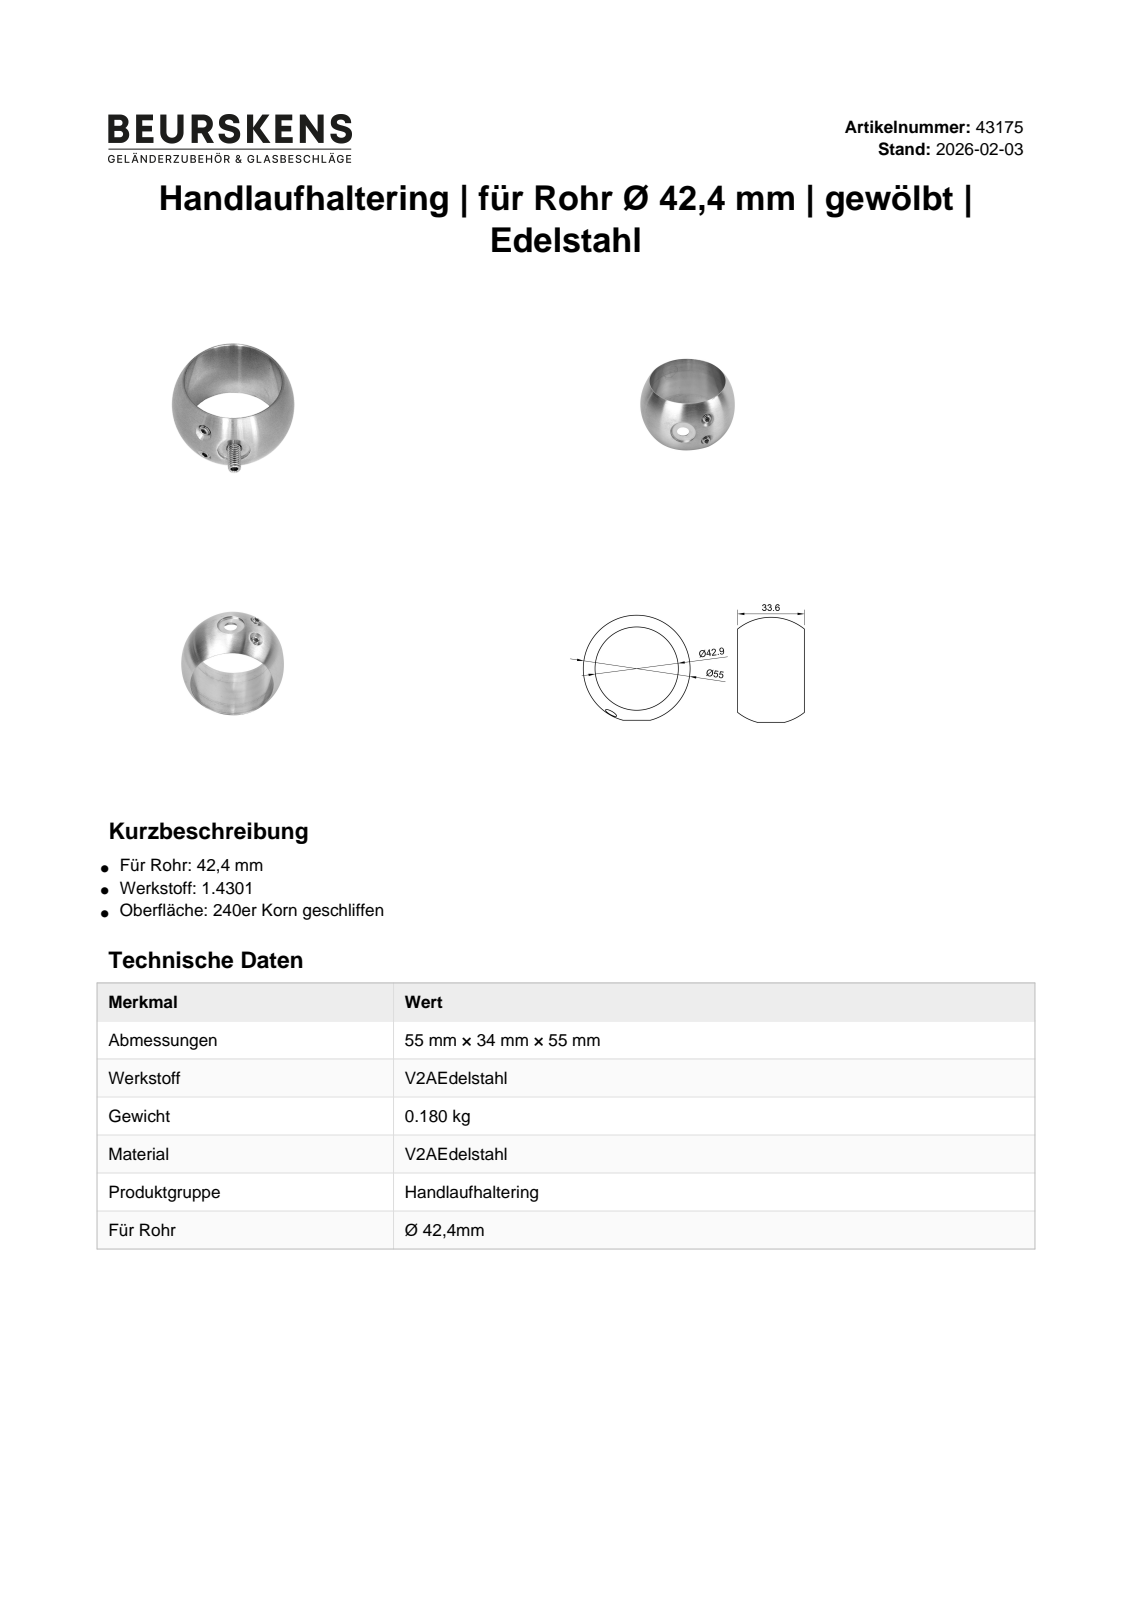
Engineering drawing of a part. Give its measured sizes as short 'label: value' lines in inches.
name: 43175
written by: Autodesk Inventor 2022 (AUTOMOTIVE_DESIGN)
unit: in
bodies: 1 solid, 12 faces (1 planar, 7 cylindrical, 4 other)
size: 2.165 × 2.129 × 1.355
volume: 1.264 in³; area: 16.56 in²
holes: 2× ⌀0.189, 1× ⌀0.256, 1× ⌀0.48, 1× ⌀0.559, 1× ⌀1.689
hole spacings: 0.63
